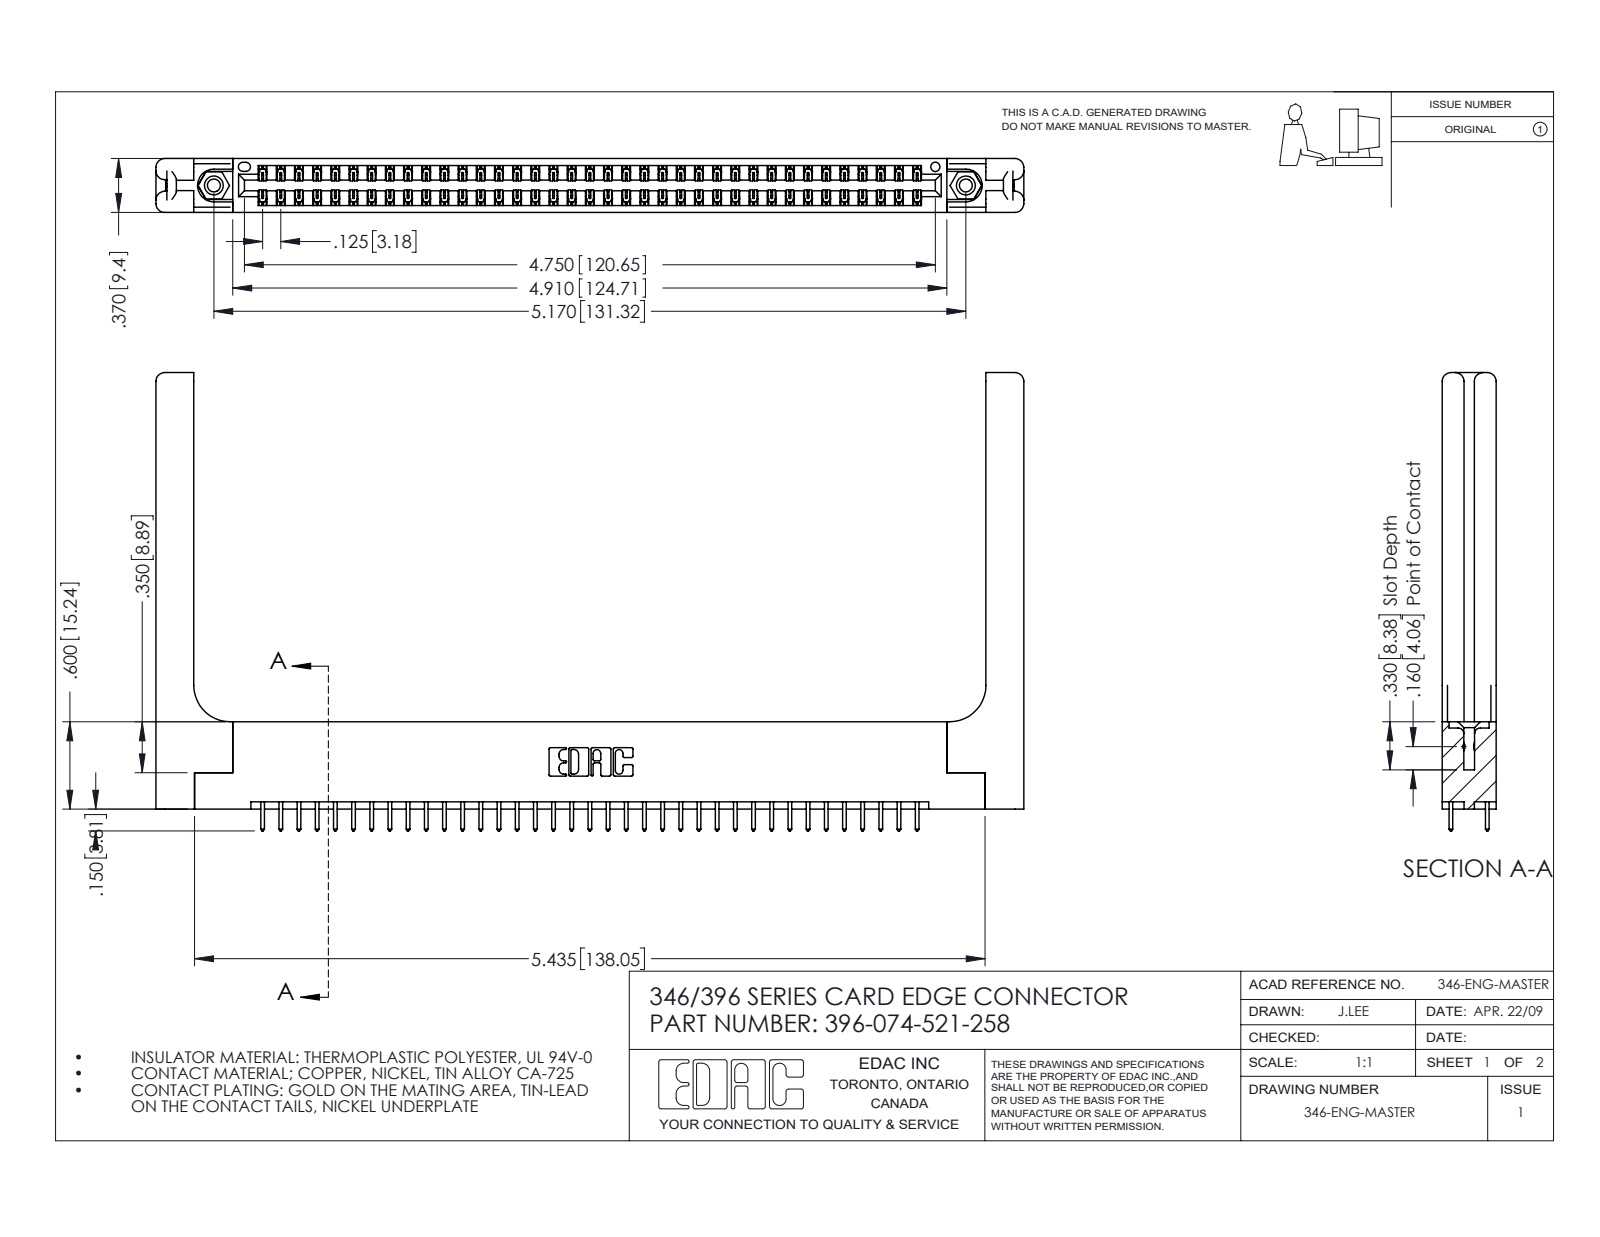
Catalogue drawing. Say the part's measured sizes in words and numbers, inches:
The part is named "345-292-001_345-293-121; 345-250-001_345-250-001-102; 346 Part_Flush Mounting Lugs - 0.156 Dia-TH; 396-074-521-258 (+1 more)". Its 3-D file was written by "SolidWorks 2016 (CONFIG_CONTROL_DESIGN)". It is 79 solids with 4226 faces: 2814 planar, 1352 cylindrical and 60 other. Overall it measures 5.966 by 3.15 by 0.37 inches. Its volume is 1.355 cubic inches and its surface area 38.61 square inches. Round holes: 2 of diameter 0.089, 2 of diameter 0.125, 2 of diameter 0.156, 1 of diameter 0.064. Round bosses or shafts: 2 of diameter 0.155. Partial cylindrical surfaces (rounded edges, fillets, slot ends): 111 of radius 0.006, 74 of radius 0.01, 22 of radius 0.01, 16 of radius 0.06, 6 of radius 0.007, 6 of radius 0.031, 3 of radius 0.026, 2 of radius 0.014. The main face-to-face distances are 0.37, 0.048, 0.322, 0.072, 0.25, 0.148, 0.15, 0.025, 0.298, 0.275. The hole center spacings are 0.246, 4.961, 5.17.
